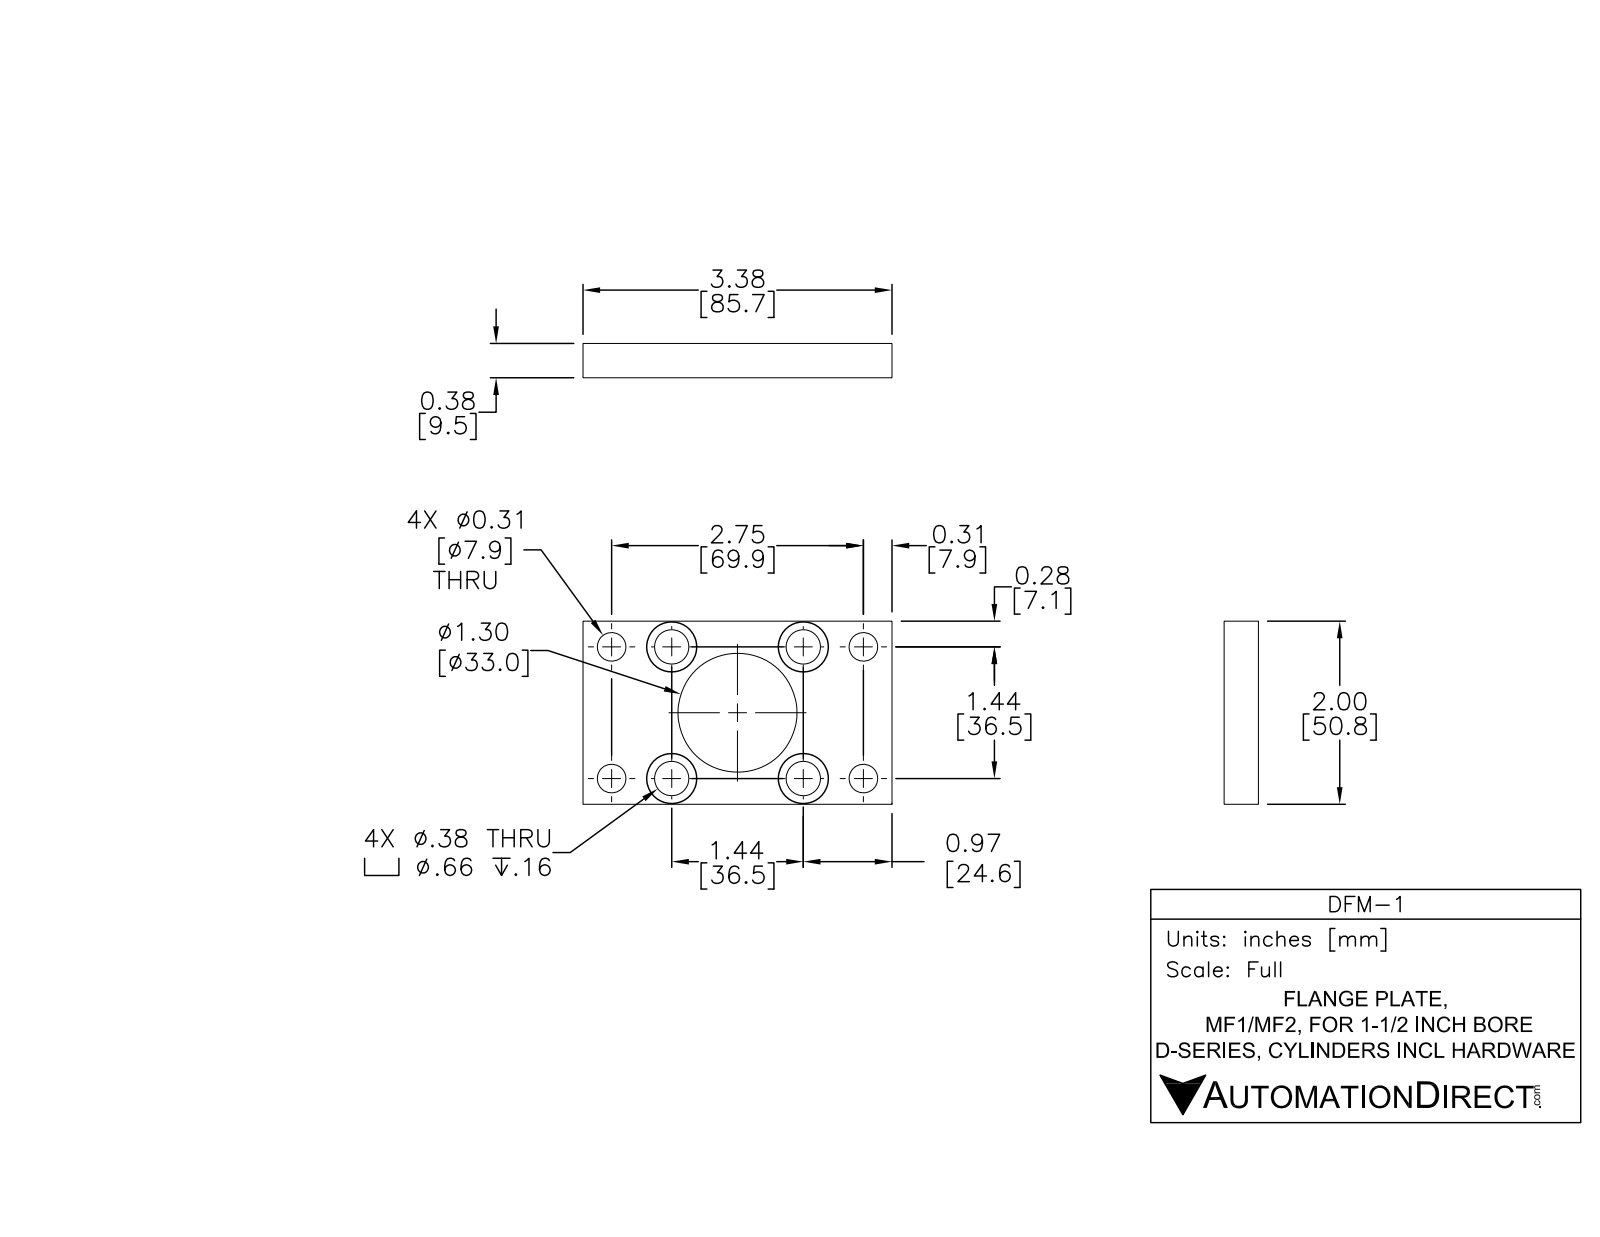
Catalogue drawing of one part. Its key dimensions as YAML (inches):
part_name: "DFM-1"
step_written_by: "SolidWorks 2015 (AUTOMOTIVE_DESIGN)"
units: inches
bodies: {solids: 1, faces: 40, planar: 10, cylindrical: 30, other: 0}
overall_size: [3.375, 2, 0.375]
volume: 1.72
surface_area: 18.6
round_holes:
  - {diameter: 0.25, count: 4}
  - {diameter: 0.313, count: 4}
  - {diameter: 0.565, count: 4}
  - {diameter: 1.3, count: 1}
face_to_face_distances: [0.375, 2, 0.155, 0.22, 3.375]
hole_center_spacings: [1.438, 1.017, 1.552, 1.58, 0.656, 2.094, 2.54, 2.033]
